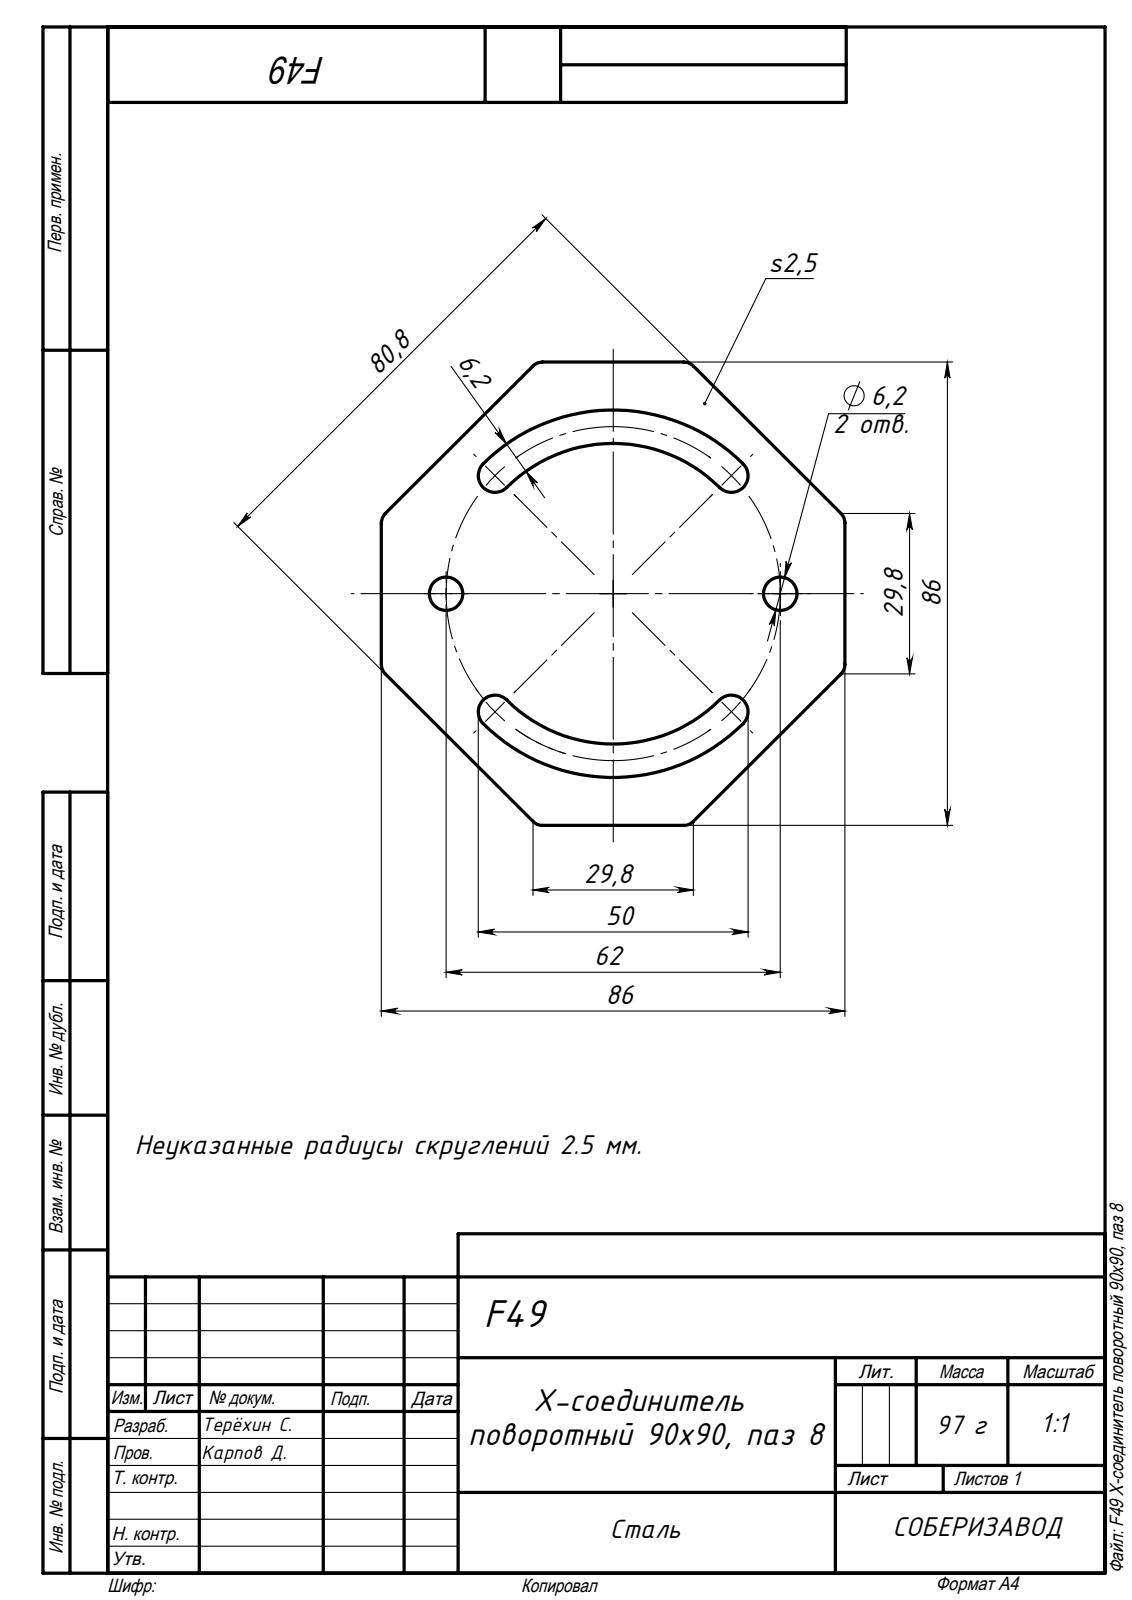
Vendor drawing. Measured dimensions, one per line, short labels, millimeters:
written by: SolidWorks 2020 (AUTOMOTIVE_DESIGN)
unit: mm
bodies: 1 solid, 32 faces (10 planar, 22 cylindrical, 0 other)
size: 86 × 86 × 2.5
volume: 12 514 mm³; area: 11 382 mm²
holes: 2× ⌀6.2
rounds: 8× R2.5, 4× R3.1, 1× R27.9, 1× R34.1
face distances: 2.5, 80.82, 86
hole spacings: 62
